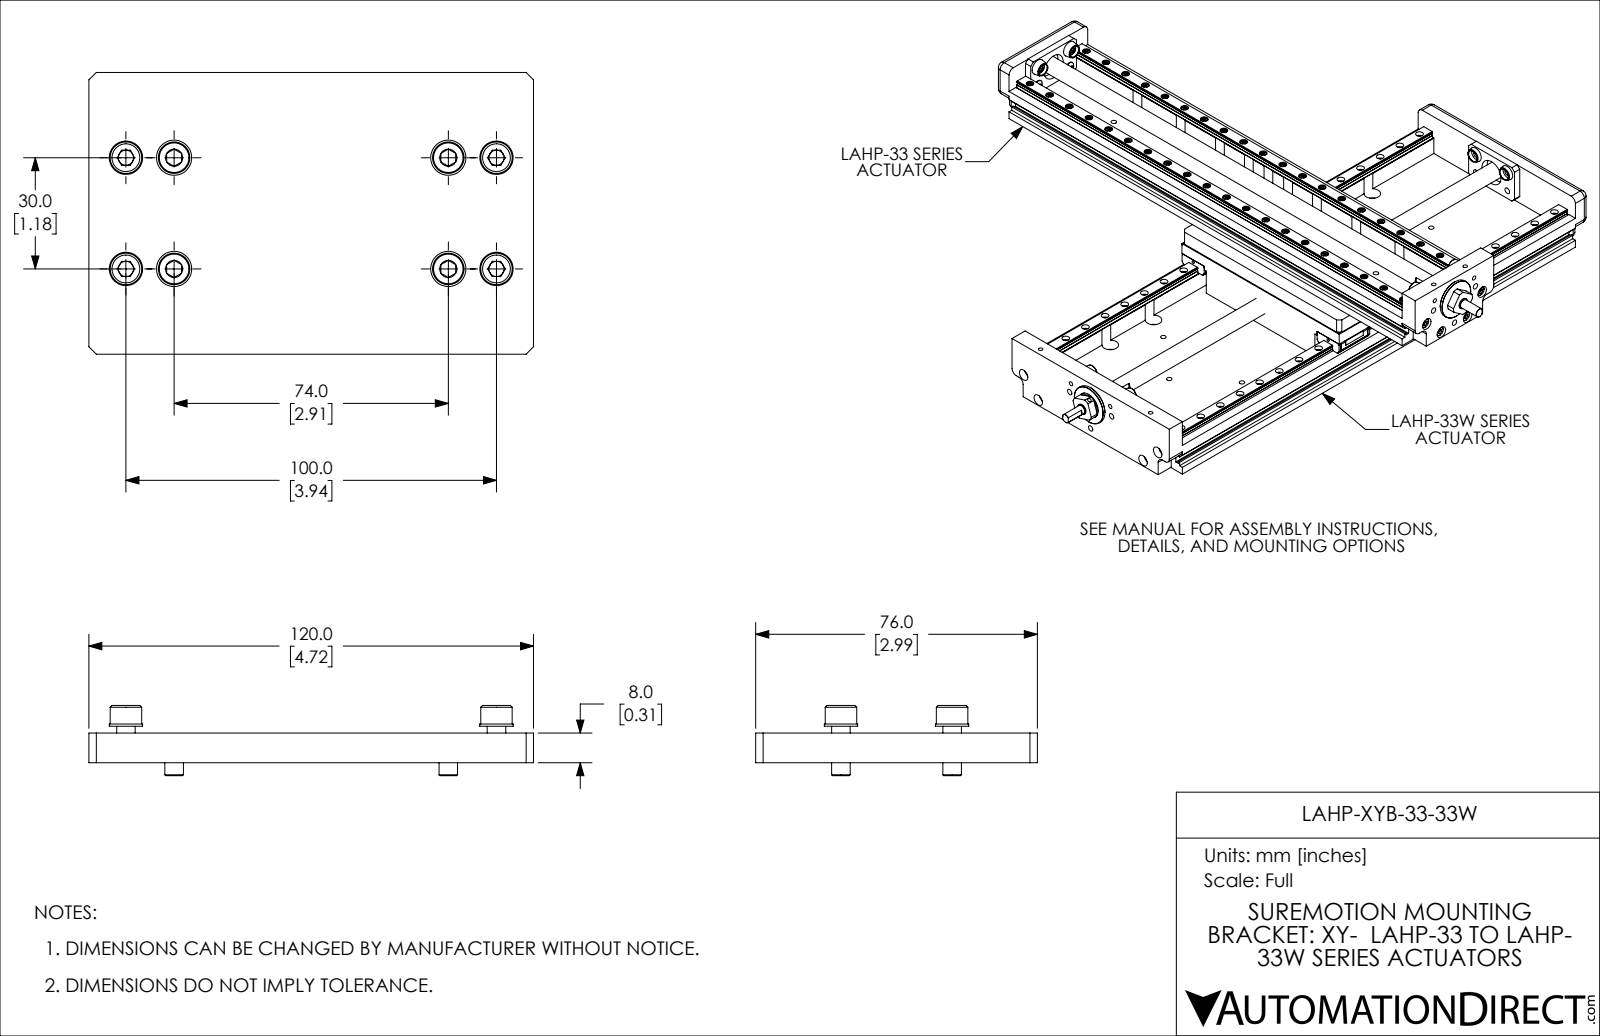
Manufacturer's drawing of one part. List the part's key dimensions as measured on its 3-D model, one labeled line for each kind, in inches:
Part name (STEP PRODUCT): LAHP-XYB-33-33W
STEP written by: SolidWorks 2019 (CONFIG_CONTROL_DESIGN)
Units: inches
Bodies: 13 solids, 278 faces (122 planar, 72 cylindrical, 84 other)
Overall size (bounding box): 4.724 × 2.992 × 0.746
Volume: 4.501 in³ · Surface area: 39.96 in²
Round holes (diameter × count): ⌀0.165 ×4, ⌀0.209 ×4, ⌀0.217 ×4, ⌀0.374 ×4
Round bosses / shafts (diameter × count): ⌀0.335 ×8, ⌀0.197 ×8, ⌀0.354 ×4
Main face-to-face distances: 0.315, 2.992, 4.724, 0.313, 0.096, 0.098, 0.217, 0.411, 0.197, 0.388
Hole centre spacings: 0.512, 1.181, 1.287, 3.425, 3.623, 2.913, 3.144, 3.937
